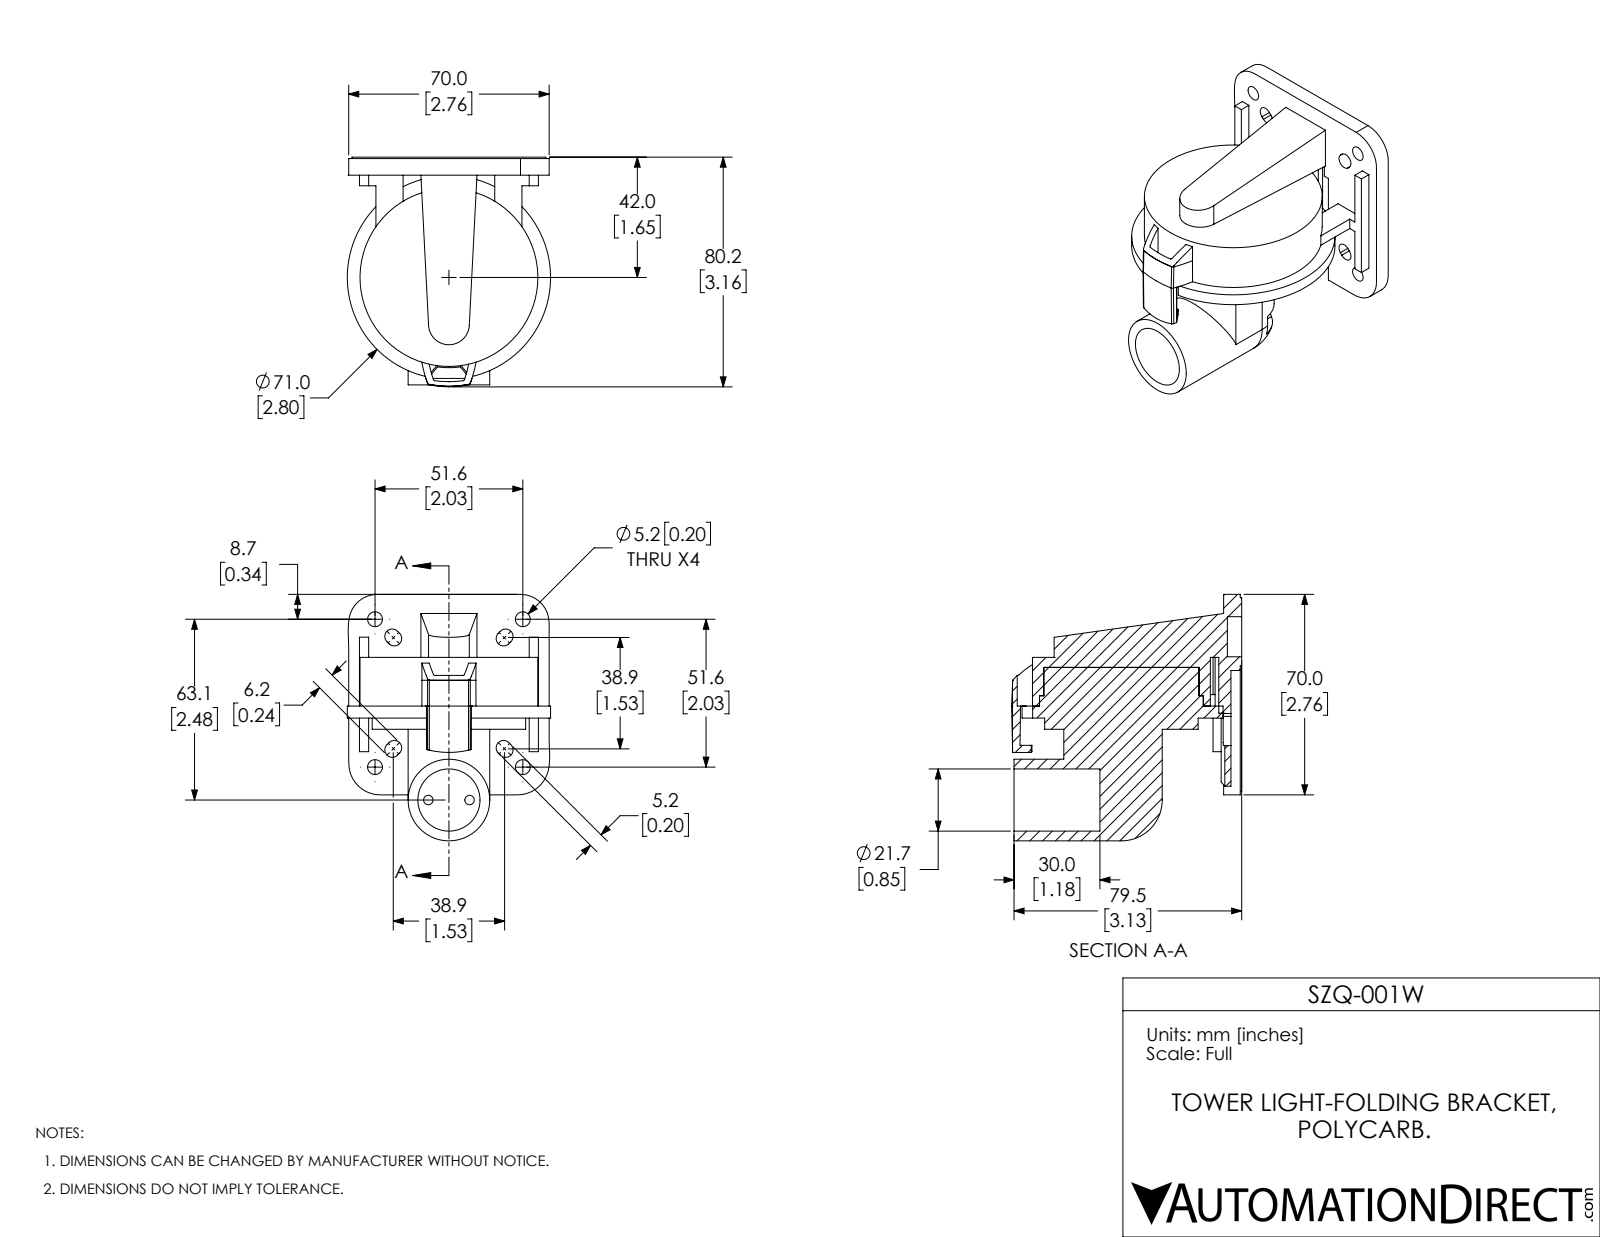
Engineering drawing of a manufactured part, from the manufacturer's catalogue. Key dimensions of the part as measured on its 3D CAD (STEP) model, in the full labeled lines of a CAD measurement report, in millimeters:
Part name (STEP PRODUCT): SZQ-001W
STEP written by: SolidWorks 2017 (AUTOMOTIVE_DESIGN)
Units: millimetres
Bodies: 2 solids, 158 faces (76 planar, 52 cylindrical, 30 other)
Overall size (bounding box): 86.1 × 80.2 × 71
Volume: 145 000 mm³ · Surface area: 47 350 mm²
Round holes (diameter × count): ⌀5.2 ×4, ⌀3.3 ×2, ⌀21.7 ×1, ⌀54.2 ×1, ⌀57.2 ×1
Round bosses / shafts (diameter × count): ⌀71 ×1, ⌀62.1 ×1, ⌀53.6 ×1, ⌀28.5 ×1
Partial cylindrical surfaces — rounded edges, fillets, slot ends (radius × count): R2.6 ×8, R31 ×2, R7.1 ×1, R30 ×1, R34 ×1, R35.7 ×1, R35.7 ×1
Main face-to-face distances: 6.3, 3.5, 17, 13.5, 17.7, 4.2, 21.2, 9.5, 3.8, 2.5
Hole centre spacings: 51.6, 7.2, 21.9, 28.2, 35, 65.8, 68.2, 71.2
